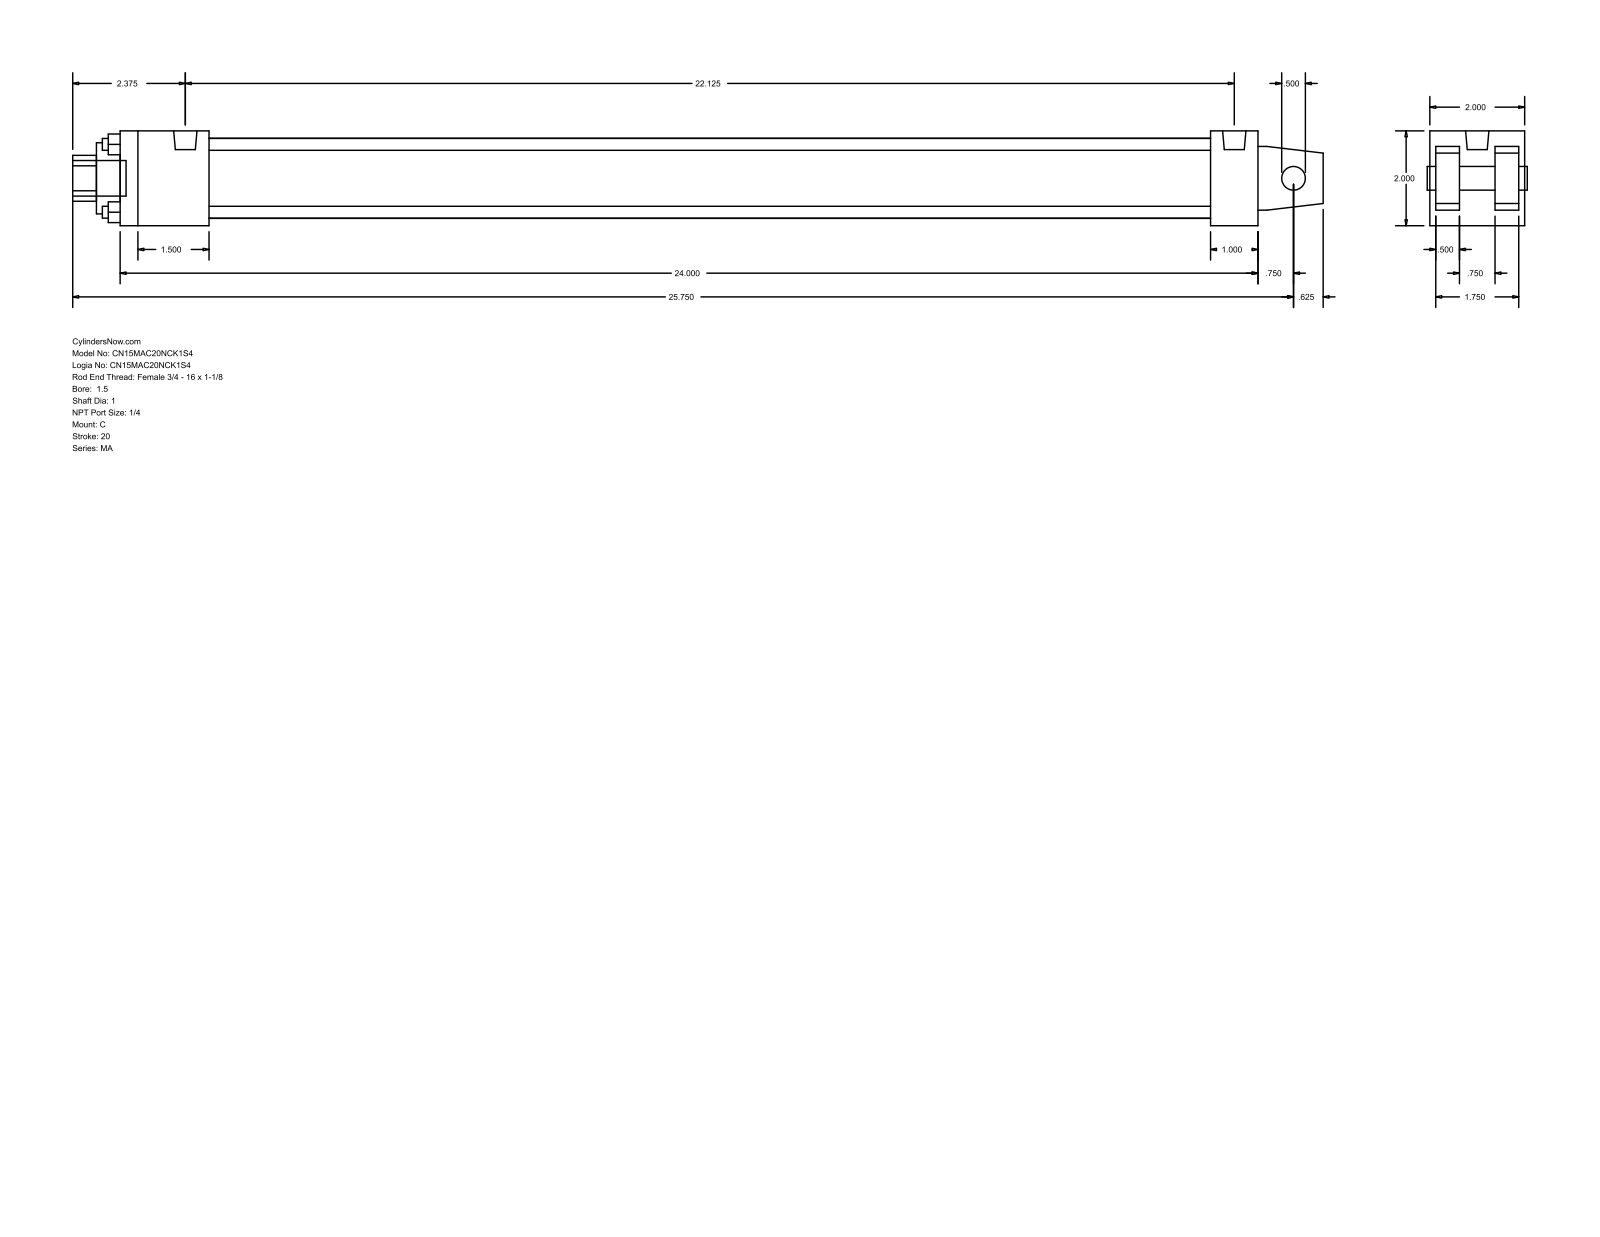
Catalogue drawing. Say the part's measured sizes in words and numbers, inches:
The part is named "MA_C__0150_1". Its 3-D file was written by "GSSL Pune (CONFIG_CONTROL_DESIGN)". It is 0 solids with 103 faces: 76 planar, 27 cylindrical and 0 other. Overall it measures 26.375 by 2 by 2 inches. Round holes: 4 of diameter 0.25, 1 of diameter 0.5, 1 of diameter 1, 1 of diameter 1.5, 1 of diameter 1.69. Round bosses or shafts: 4 of diameter 0.313, 2 of diameter 0.492, 1 of diameter 0.75. Partial cylindrical surfaces (rounded edges, fillets, slot ends): 1 of radius 0.484. The main face-to-face distances are 2, 1.875, 0.5, 0.125, 0.625, 1.375, 1.25, 1.75, 24, 1. The hole center spacings are 1.011, 1.43, 2.022.
